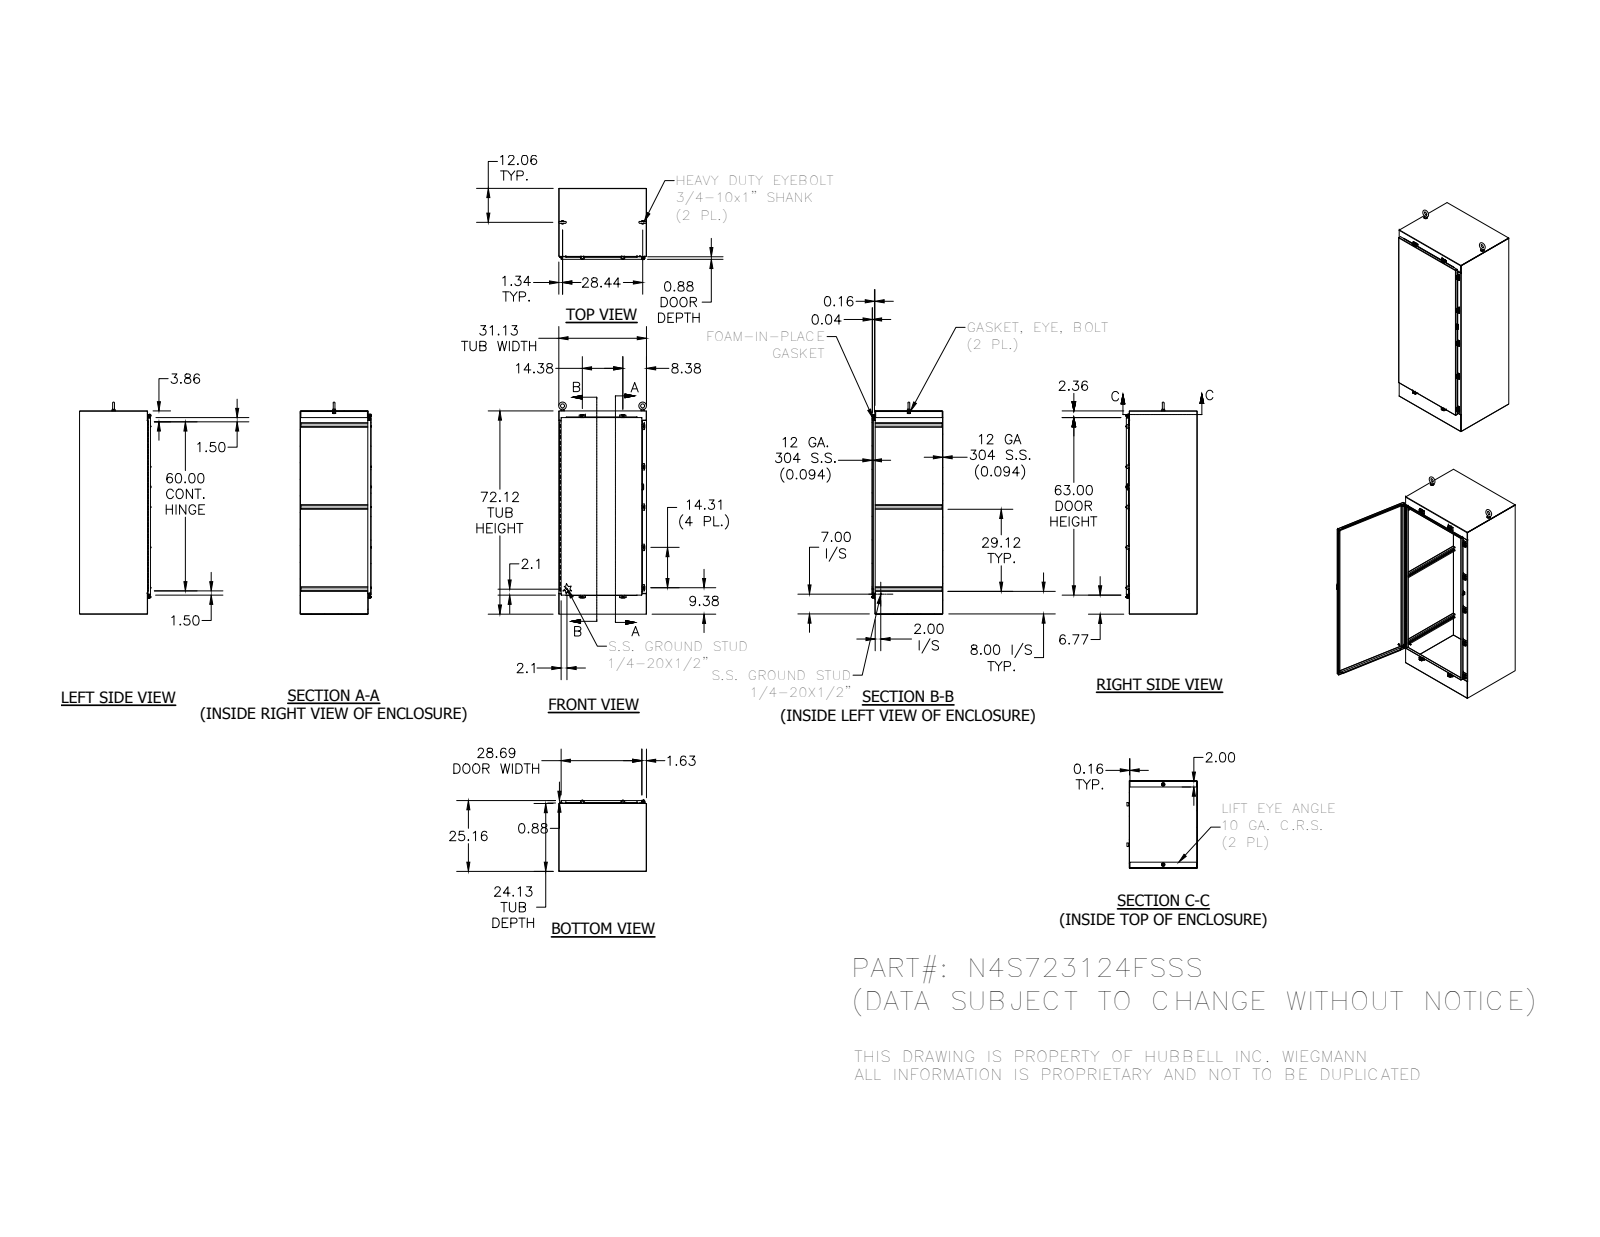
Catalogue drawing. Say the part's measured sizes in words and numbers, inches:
The part is named "30824-1_1; 30824-4_1; 3063_1; HSSN1300W60T_1 (+8 more)". Its 3-D file was written by "SolidWorks 2014 (AUTOMOTIVE_DESIGN)". It is 78 solids with 3000 faces: 1210 planar, 1210 cylindrical and 580 other. Overall it measures 75.248 by 31.125 by 25.355 inches. Its volume is 1 115 cubic inches and its surface area 22 989 square inches. Round holes: 9 of diameter 0.211, 9 of diameter 0.281, 9 of diameter 0.3, 3 of diameter 0.11, 2 of diameter 0.642, 2 of diameter 0.813, 1 of diameter 0.125, 1 of diameter 0.156, 1 of diameter 0.5. Round bosses or shafts: 12 of diameter 0.25, 9 of diameter 0.52, 9 of diameter 0.5, 9 of diameter 0.35, 2 of diameter 1.25, 2 of diameter 1.12, 2 of diameter 0.75, 2 of diameter 0.337. Partial cylindrical surfaces (rounded edges, fillets, slot ends): 107 of radius 0.03, 43 of radius 0.125, 22 of radius 0.062, 21 of radius 0.25, 19 of radius 0.031, 18 of radius 0.019, 18 of radius 0.053, 18 of radius 0.086. The main face-to-face distances are 0.094, 25.067, 31.031, 24.973, 25.161, 30.938, 31.125, 72.031, 24.031, 1.035. The hole center spacings are 14.313, 28.626, 0.789, 14.38, 42.939, 64.375, 65.961, 0.449.
